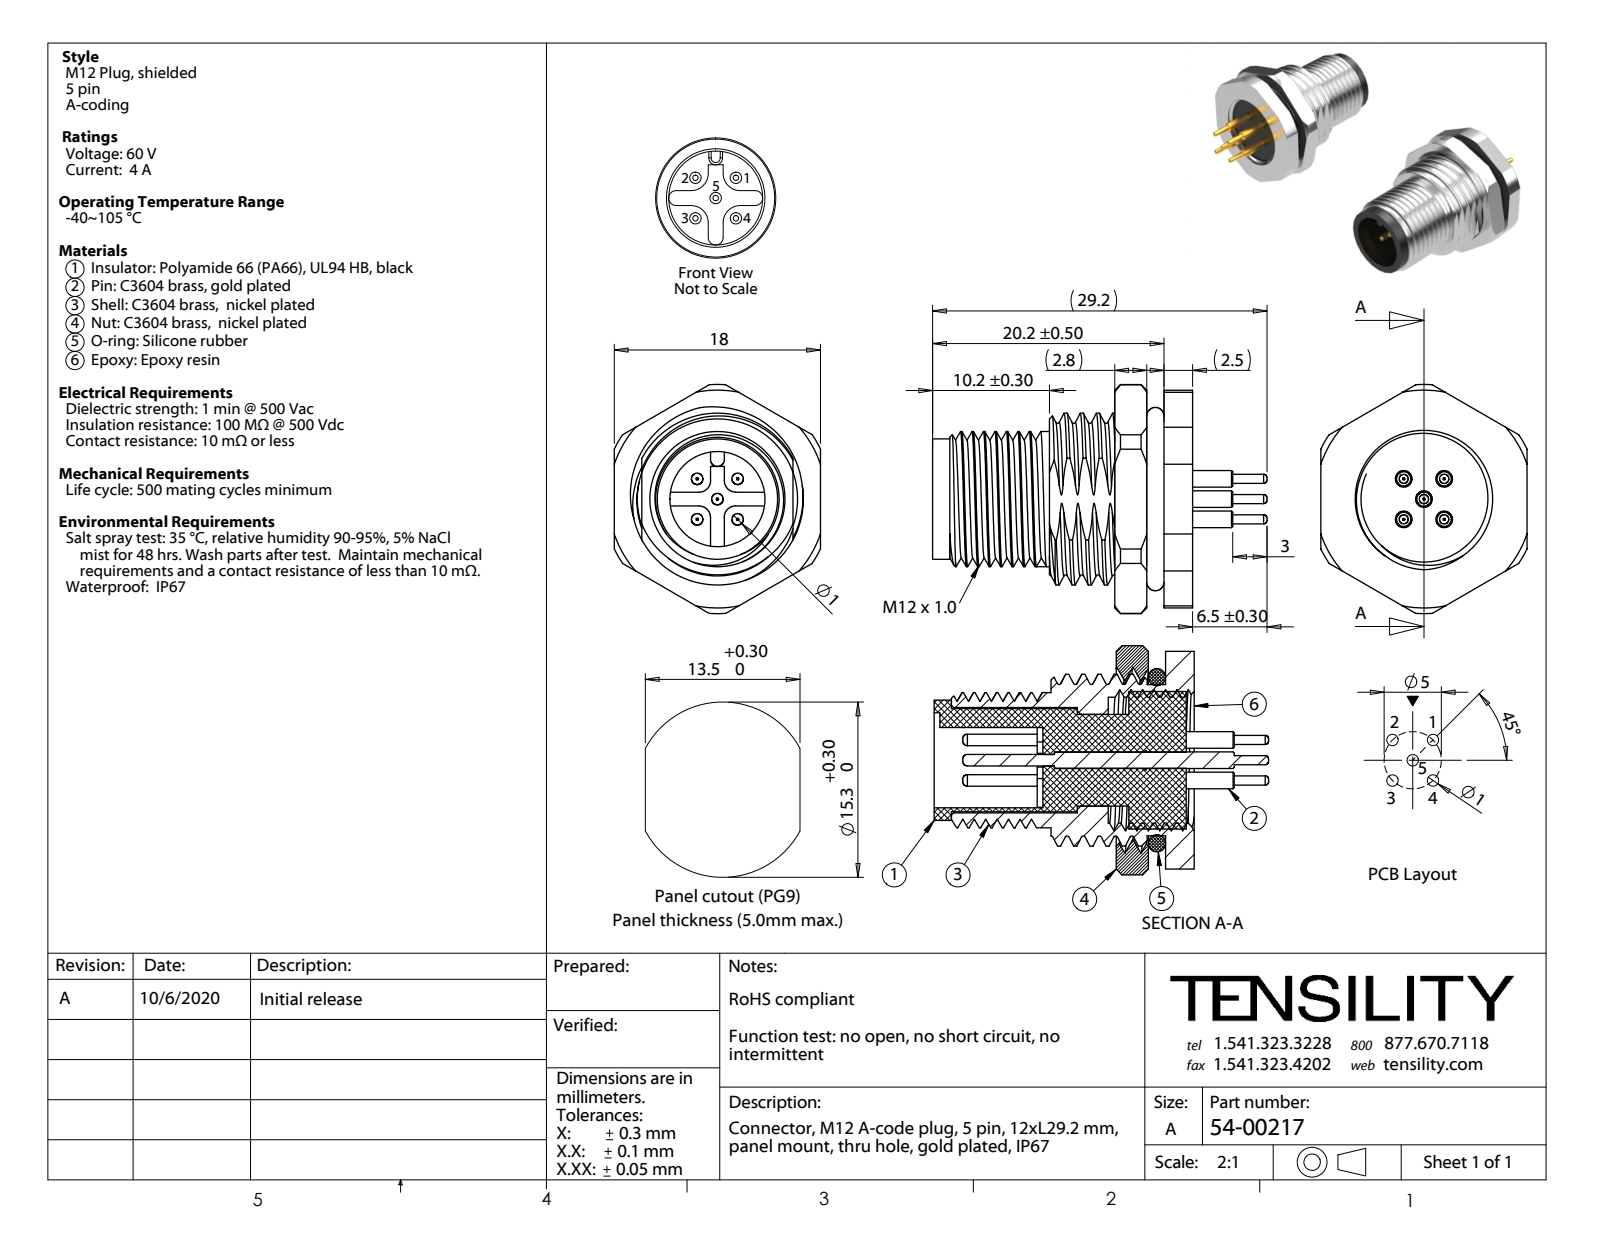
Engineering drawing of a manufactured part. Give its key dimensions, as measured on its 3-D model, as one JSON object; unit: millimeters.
{"part_name": "54-00217-02; 54-00217-04; 54-00217-01; 54-00217 (+2 more)", "step_written_by": "SolidWorks 2015 (CONFIG_CONTROL_DESIGN)", "units": "millimeters", "bodies": {"solids": 9, "faces": 375, "planar": 84, "cylindrical": 149, "other": 142}, "overall_size": [29.2, 20, 18], "volume_mm3": 2957, "surface_area_mm2": 5481, "round_holes": [[1, 5], [1.4, 5], [8, 1], [8.3, 1], [9.2, 1], [11, 1], [14, 1]], "round_bosses_or_shafts": [[1.45, 5], [0.8, 5], [13.2, 1], [12, 1], [11.8, 1], [10.5, 1], [9, 1]], "partial_cylinders_radius": [[1, 4], [0.6, 1], [7.5, 1], [9.5, 1], [10, 1]], "face_to_face_distances": [6.8, 0.7, 1.8, 5, 2.5, 1.5, 5.7, 18, 7.5, 6.1], "hole_center_spacings": [2.5, 3.54, 5.01]}
